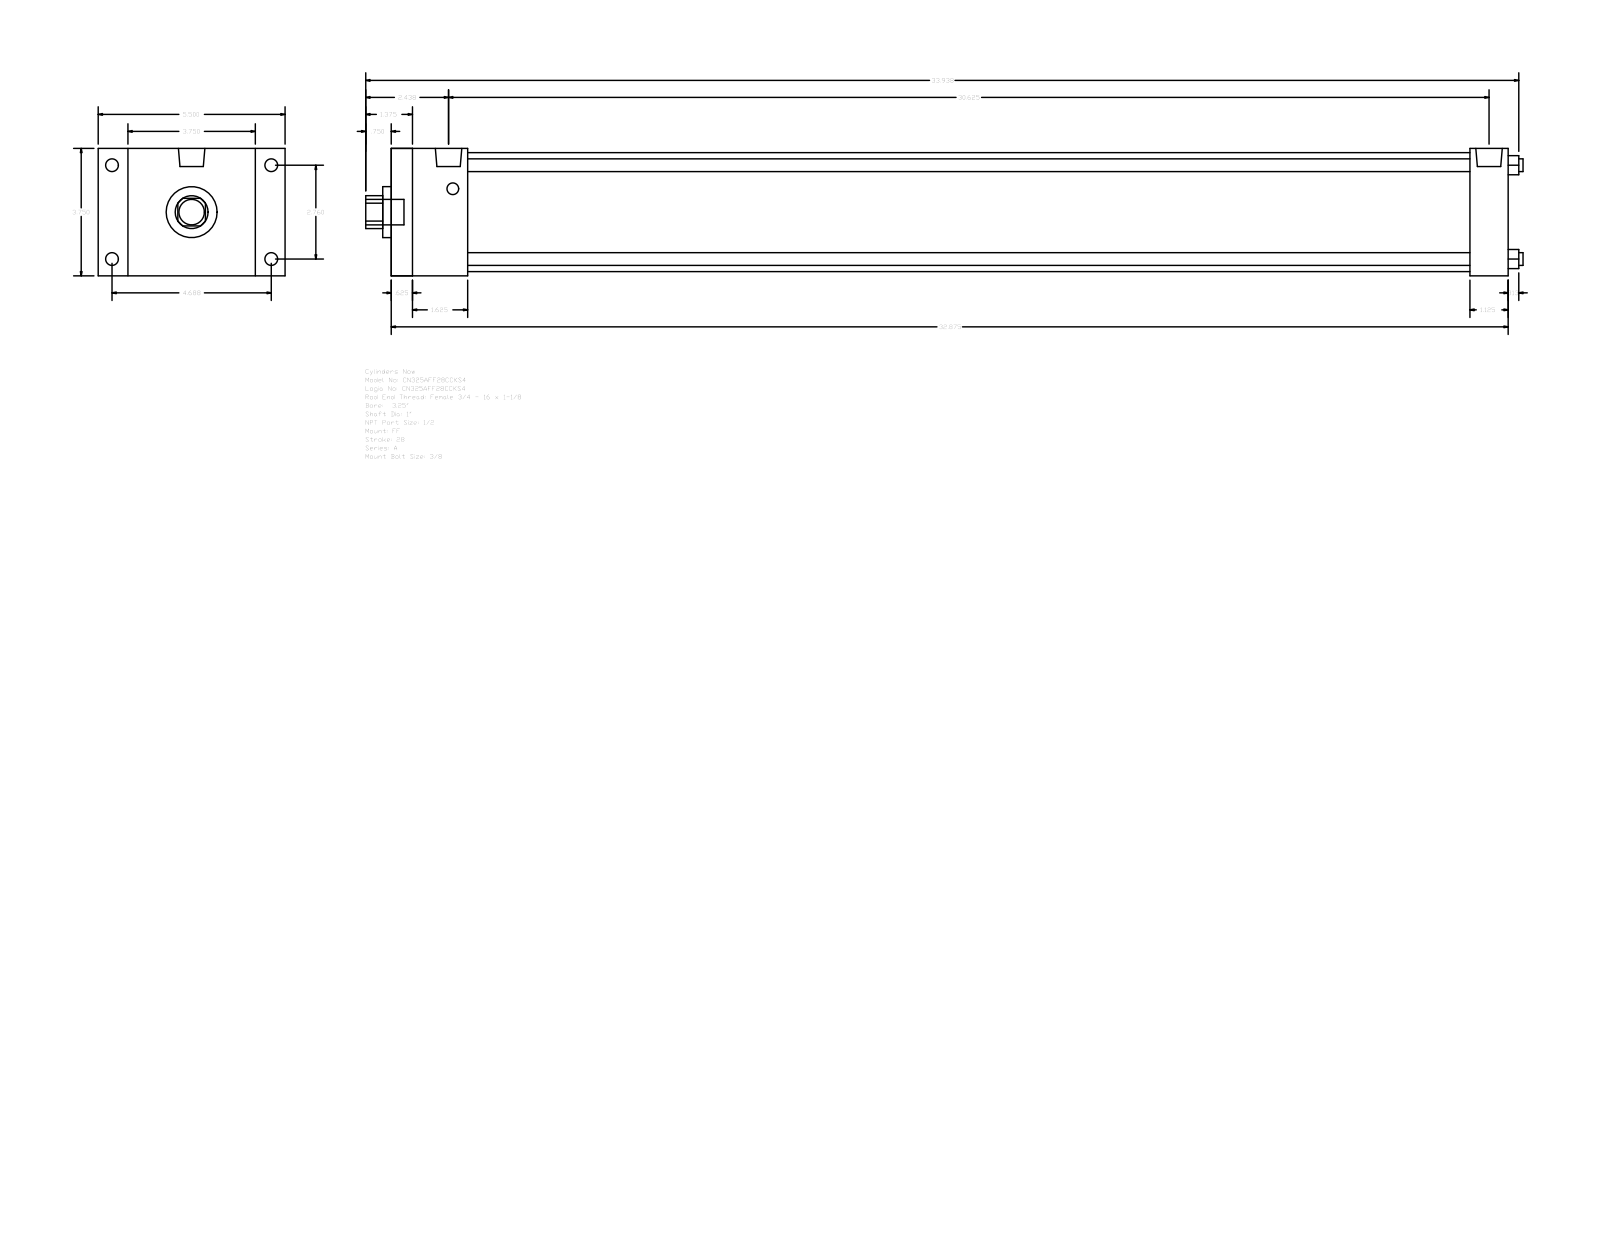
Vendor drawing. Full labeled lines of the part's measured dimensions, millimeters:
Part name (STEP PRODUCT): A_FF__0325_1
STEP written by: GSSL Pune (CONFIG_CONTROL_DESIGN)
Units: millimetres
Bodies: 0 solids, 92 faces (64 planar, 28 cylindrical, 0 other)
Overall size (bounding box): 865.19 × 139.7 × 95.25
Round holes (diameter × count): ⌀9.53 ×4, ⌀25.4 ×1, ⌀38.1 ×1, ⌀88.9 ×1
Round bosses / shafts (diameter × count): ⌀9.53 ×4, ⌀8.73 ×4, ⌀19.77 ×2, ⌀19.05 ×1
Partial cylindrical surfaces — rounded edges, fillets, slot ends (radius × count): R12.29 ×1
Main face-to-face distances: 95.24, 835.03, 15.87, 819.16, 22.23, 117.47, 57.15, 806.45, 41.28, 790.58
Hole centre spacings: 49.57, 70.1, 99.14
